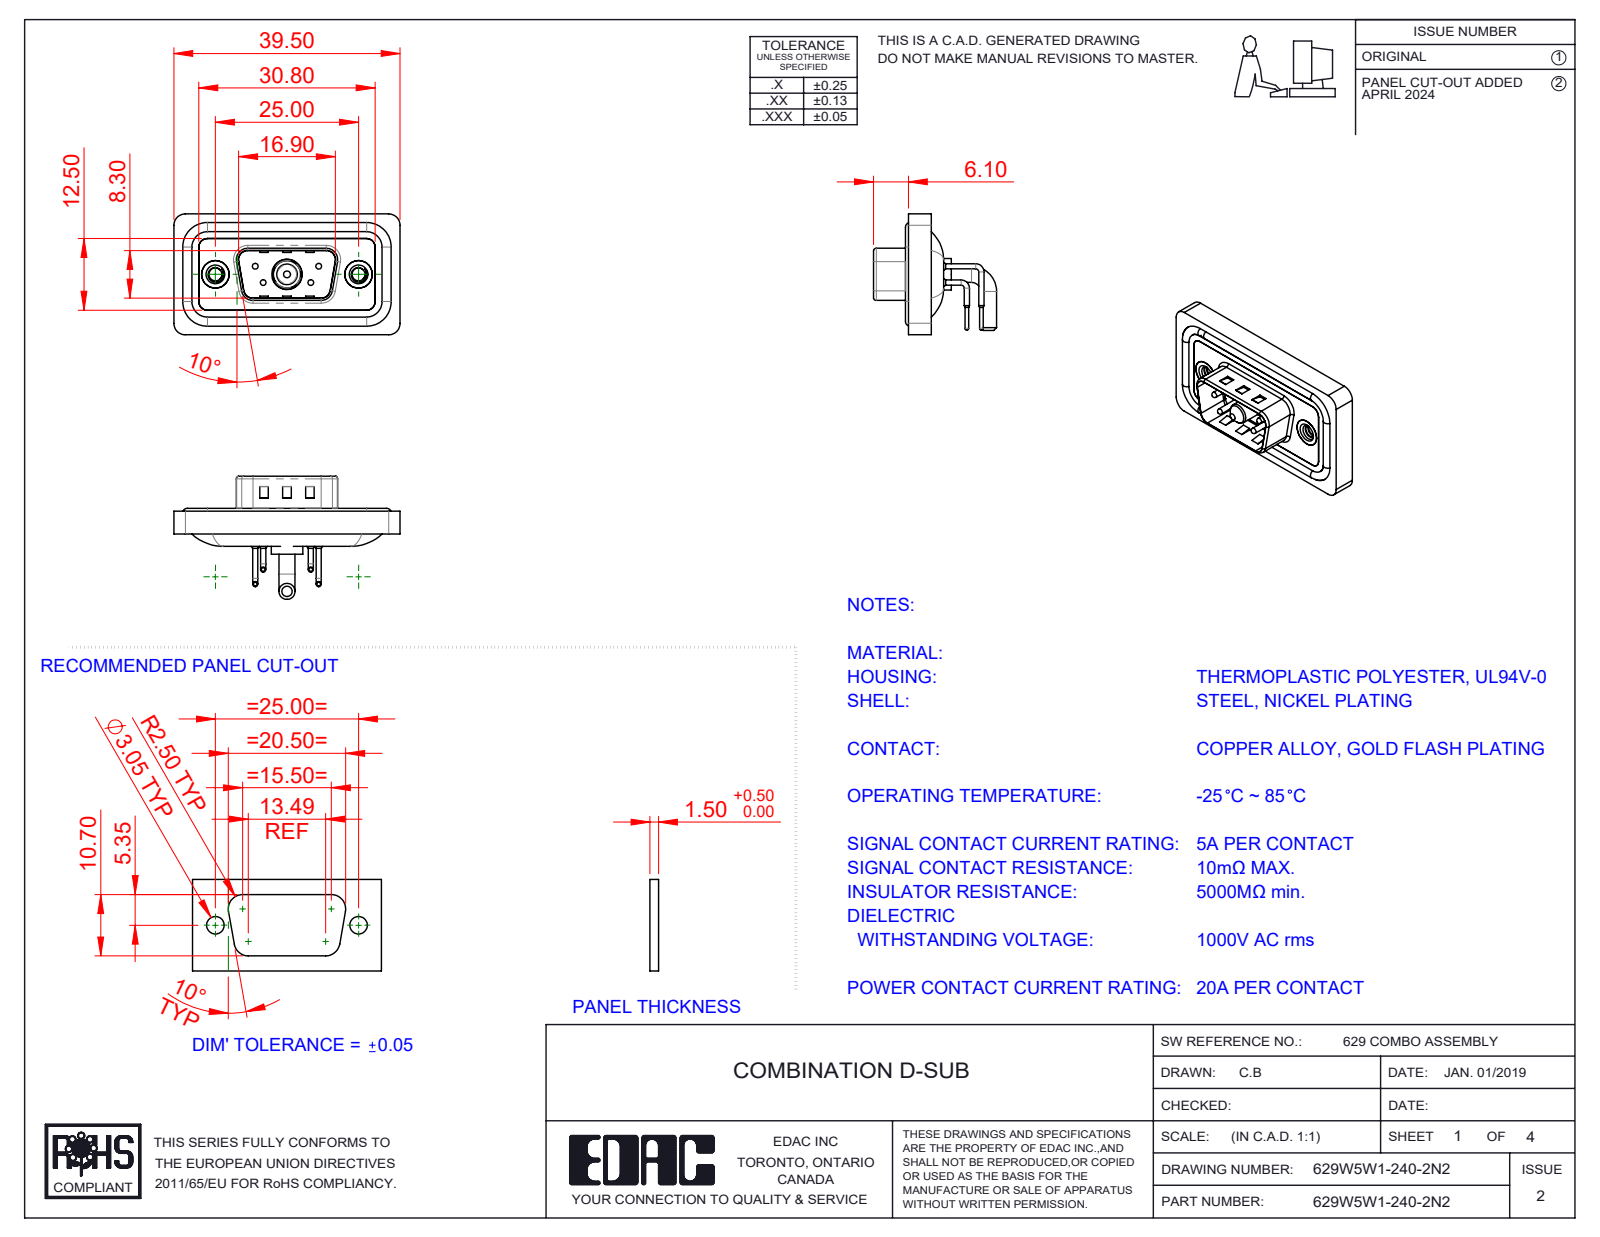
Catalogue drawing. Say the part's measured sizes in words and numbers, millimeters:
The part is named "Power Pin_20A RA; 629Combo Contact Row 2; 629Combo Housing_5W1; 629W5W1-140-2N2 (+5 more)". Its 3-D file was written by "SolidWorks 2023 (CONFIG_CONTROL_DESIGN)". It is 13 solids with 894 faces: 411 planar, 345 cylindrical and 138 other. Overall it measures 39.5 by 21.5 by 21.1 millimeters. Its volume is 4 487 cubic millimeters and its surface area 7 164 square millimeters. Round holes: 4 of diameter 0.75, 4 of diameter 1.6, 4 of diameter 2, 2 of diameter 2.26, 2 of diameter 4, 2 of diameter 4.8, 2 of diameter 5, 1 of diameter 4.85, 1 of diameter 5.3. Round bosses or shafts: 8 of diameter 0.9, 4 of diameter 1.6, 4 of diameter 1.5, 4 of diameter 1, 4 of diameter 0.65, 2 of diameter 4.9, 2 of diameter 2.8, 1 of diameter 5.5. Partial cylindrical surfaces (rounded edges, fillets, slot ends): 18 of radius 1.5, 18 of radius 2, 8 of radius 0.5, 8 of radius 1.6, 4 of radius 0.25, 4 of radius 0.6, 4 of radius 0.65, 4 of radius 0.9. The main face-to-face distances are 0.4, 2.9, 1.1, 0.8, 2.1, 2.5, 1.6, 3.1, 4.5, 1.5. The hole center spacings are 3.16, 5.72, 7.1, 12.5, 18.1, 4.39, 4.4, 8.31.
